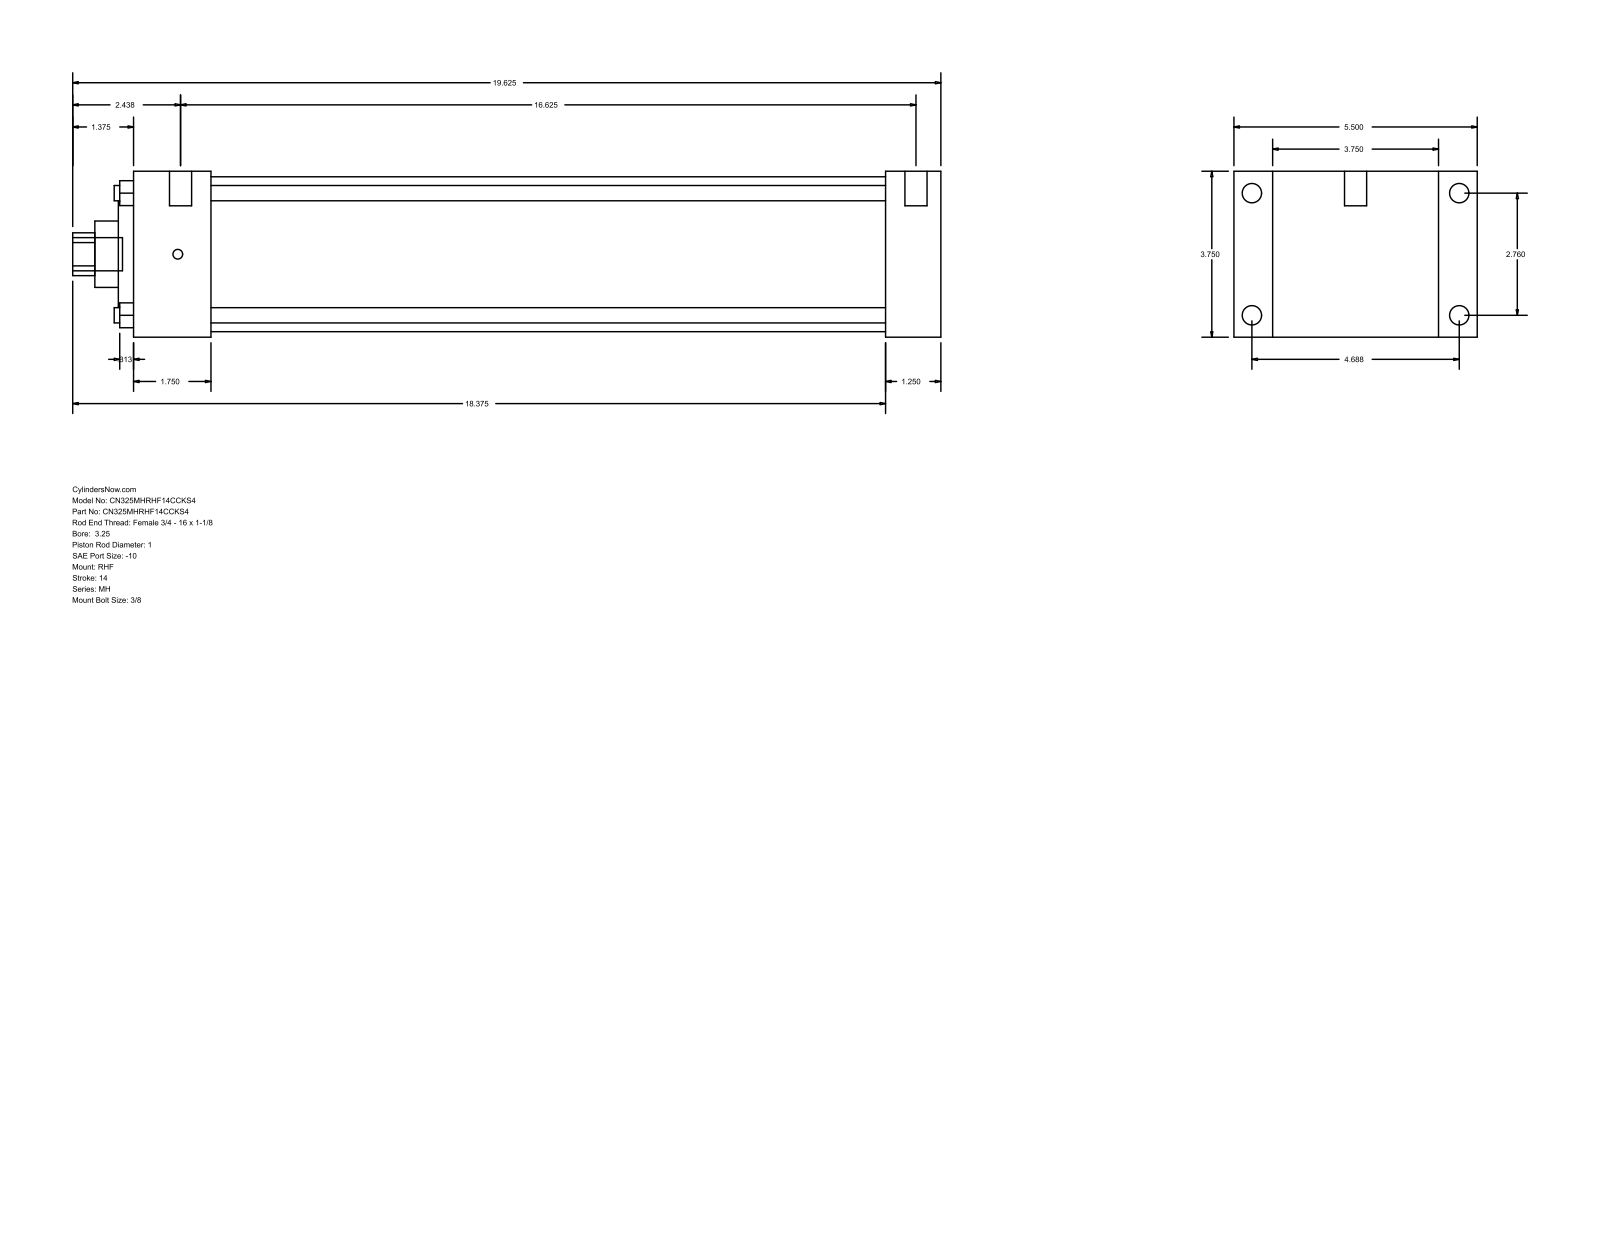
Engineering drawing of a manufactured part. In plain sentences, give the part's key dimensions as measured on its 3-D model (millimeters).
The part is named "MH_RHF__0325_1". Its 3-D file was written by "GSSL Pune (CONFIG_CONTROL_DESIGN)". It is 0 solids with 90 faces: 61 planar, 29 cylindrical and 0 other. Overall it measures 498.48 by 139.7 by 95.25 millimeters. Round holes: 4 of diameter 8.76, 1 of diameter 25.4, 1 of diameter 38.1, 1 of diameter 60.33, 1 of diameter 88.9. Round bosses or shafts: 4 of diameter 11.13, 4 of diameter 5.56, 2 of diameter 12.7, 1 of diameter 19.05. Partial cylindrical surfaces (rounded edges, fillets, slot ends): 1 of radius 12.29. The main face-to-face distances are 95.24, 31.75, 22.23, 117.47, 431.81, 463.56, 139.7, 44.46, 387.35, 419.1. The hole center spacings are 49.57, 70.1, 99.14.
